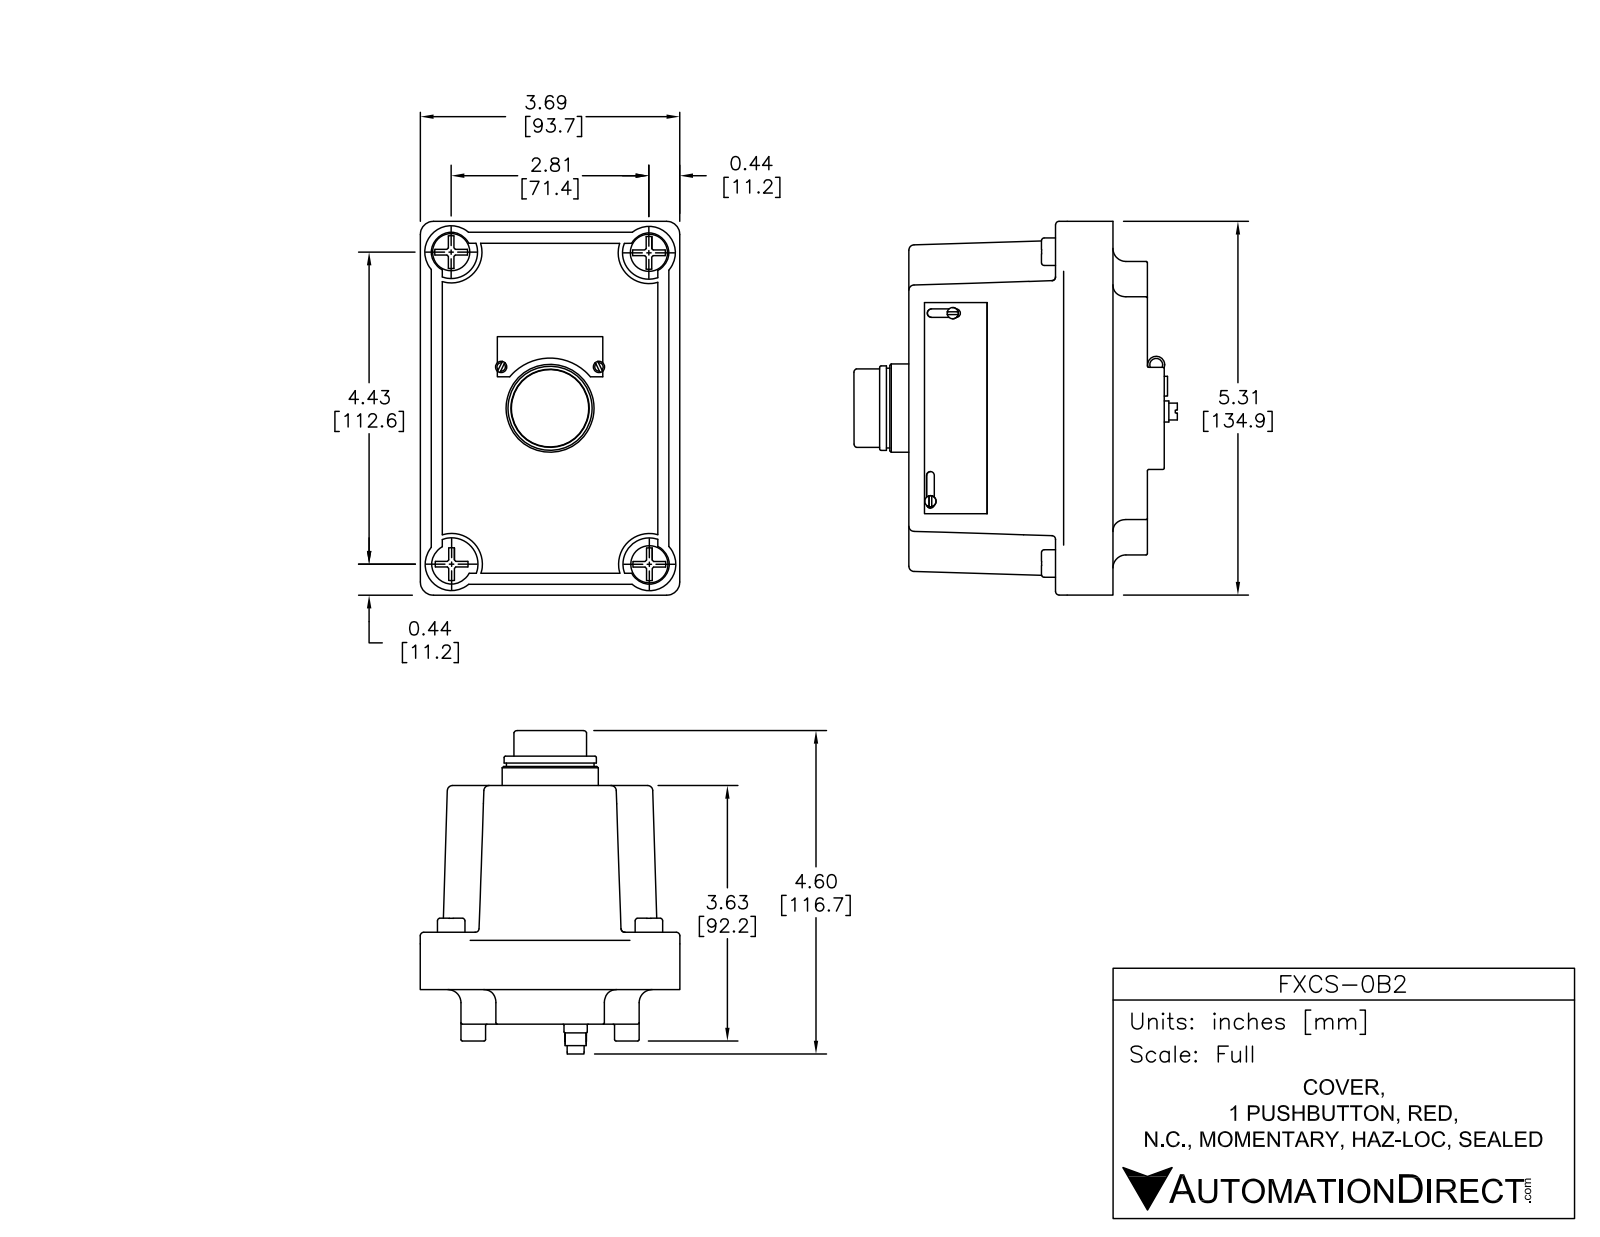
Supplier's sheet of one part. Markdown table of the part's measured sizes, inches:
| quantity | value |
| --- | --- |
| part name | FXCS-0B2 |
| STEP written by | SolidWorks 2015 (AUTOMOTIVE_DESIGN) |
| units | inches |
| bodies | 2 solids, 677 faces (275 planar, 145 cylindrical, 257 other) |
| overall size | 5.31 × 4.565 × 3.69 |
| volume | 48.65 in³ |
| surface area | 96.02 in² |
| round holes (diameter × count) | 0.16 × 8, 0.198 × 1, 1.155 × 1 |
| round bosses / shafts (diameter × count) | 0.16 × 6, 0.39 × 4, 1.375 × 1, 1.3 × 1, 1.04 × 1, 0.33 × 1, 0.3 × 1, 0.24 × 1 |
| partial cylindrical surfaces (radius × count) | 0.02 × 22, 0.05 × 12, 0.055 × 4, 0.06 × 4, 0.075 × 4, 0.185 × 4, 0.42 × 4, 0.653 × 3 |
| main face-to-face distances | 3.39, 0.49, 2.9, 0.02, 3.69, 0.578, 3.111, 1.19, 0.7, 2.2 |
| hole center spacings | 0.25, 2.197, 0.5, 2.183, 2.239, 0.75, 1.092, 1.115 |
